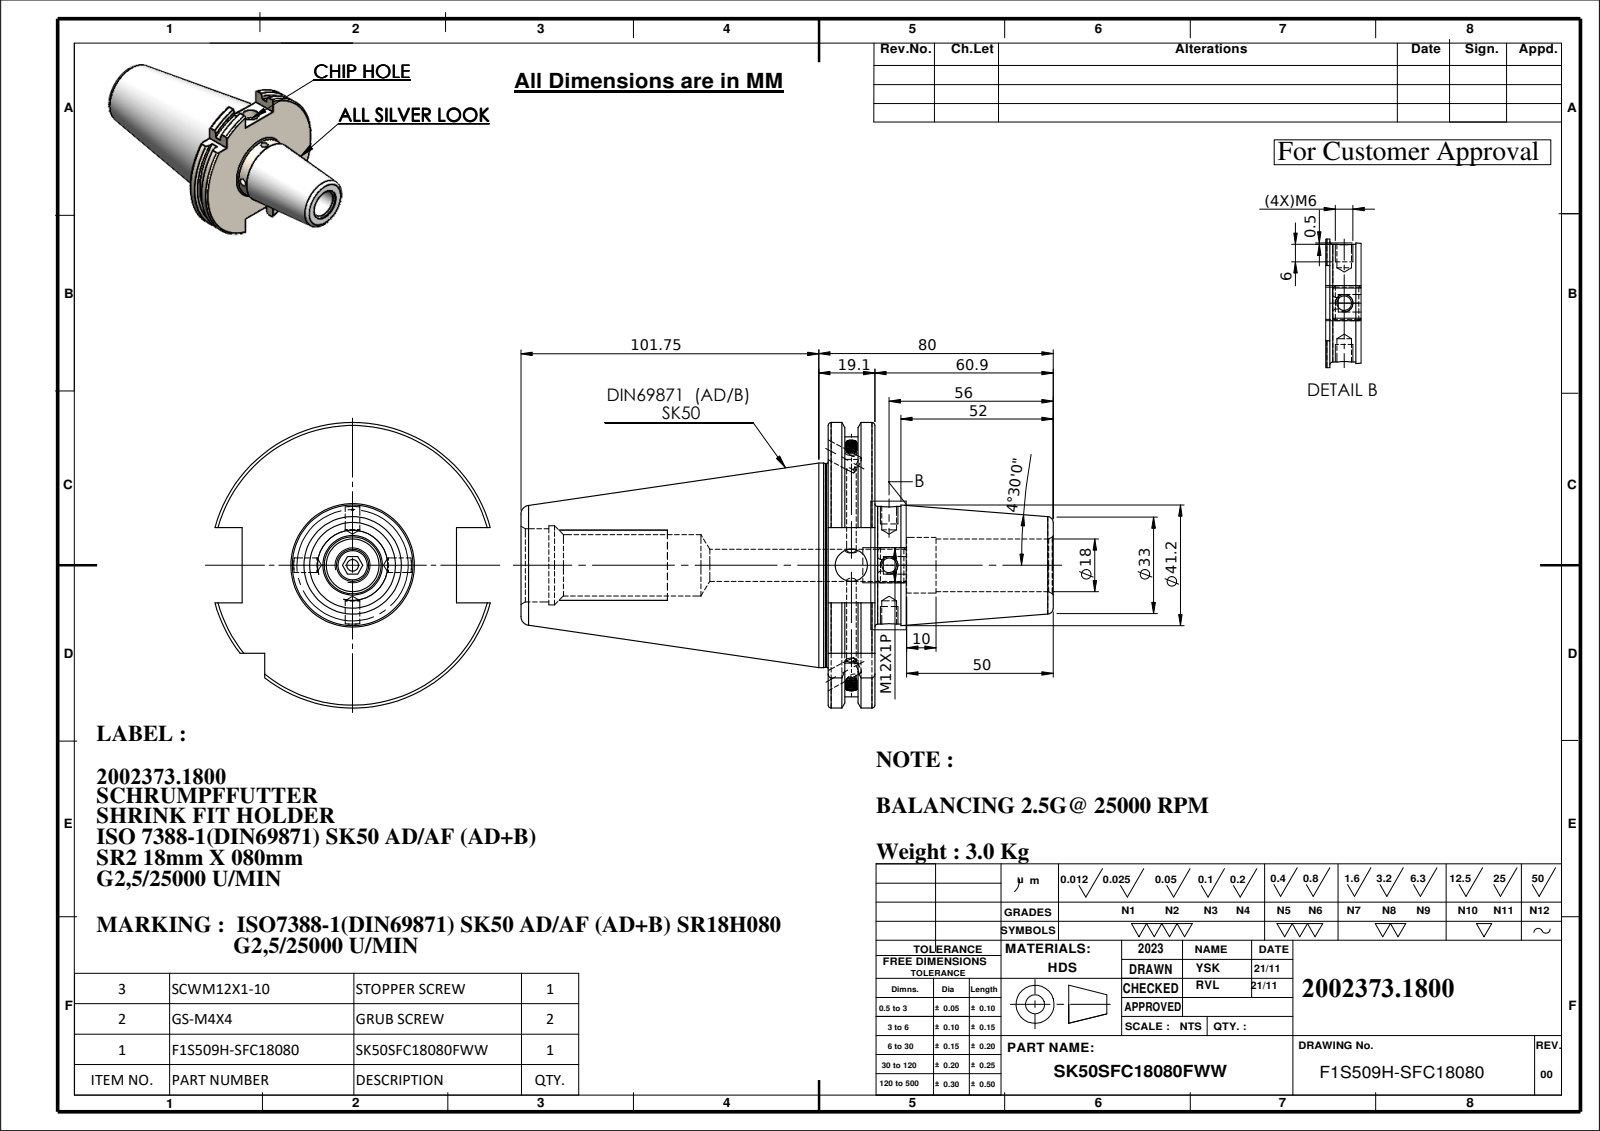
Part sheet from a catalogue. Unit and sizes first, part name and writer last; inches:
Units: inches
Overall size (bounding box): 7.156 × 3.839 × 3.703
Round holes (diameter × count): ⌀0.197 ×2, ⌀0.236 ×2, ⌀0.433 ×2, ⌀0.13 ×1, ⌀0.157 ×1, ⌀0.709 ×1, ⌀0.748 ×1, ⌀0.827 ×1, ⌀0.984 ×1, ⌀1.063 ×1
Round bosses / shafts (diameter × count): ⌀0.157 ×2, ⌀2.75 ×1, ⌀2.734 ×1, ⌀1.582 ×1, ⌀0.472 ×1
Partial cylindrical surfaces — rounded edges, fillets, slot ends (radius × count): R1.768 ×1, R1.919 ×1
Main face-to-face distances: 0.626, 0.223, 0.403, 0.399, 0.176, 0.227, 4.132, 4.355, 4.531, 4.758
Hole centre spacings: 0.508
Volume: 23.55 in³ · Surface area: 85.16 in²
Bodies: 4 solids, 242 faces (53 planar, 77 cylindrical, 112 other)
Part name (STEP PRODUCT): GS-M4X4_DIN 913 - M4 x 4-N; SCWM12X1-10; SK50SFC18080FWW; F1S509H-SFC18080
STEP written by: SolidWorks 2023 (CONFIG_CONTROL_DESIGN)
